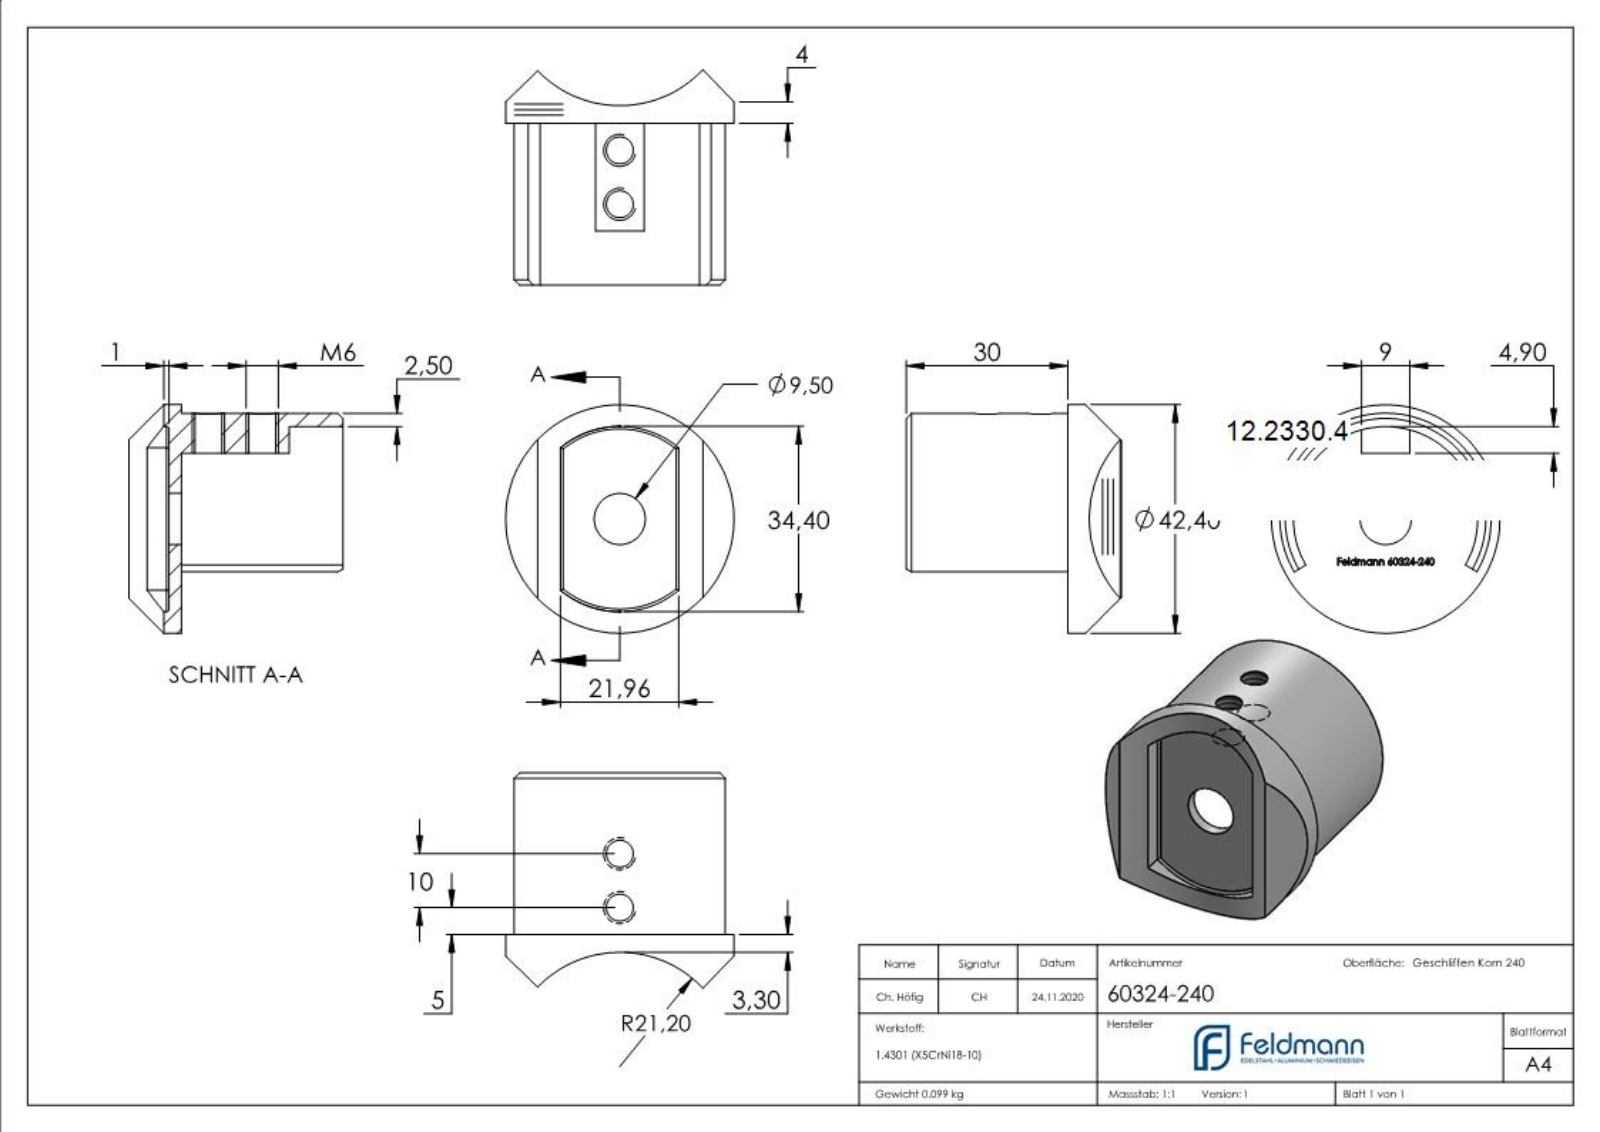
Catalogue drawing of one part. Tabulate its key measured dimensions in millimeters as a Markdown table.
| quantity | value |
| --- | --- |
| part name | 60324-240 |
| STEP written by | SolidWorks 2018 (CONFIG_CONTROL_DESIGN) |
| units | millimeters |
| bodies | 1 solid, 323 faces (173 planar, 19 cylindrical, 131 other) |
| overall size | 42.4 × 42.4 × 39.97 |
| volume | 12 588 mm³ |
| surface area | 9 048 mm² |
| round holes (diameter × count) | 5 × 2, 9.5 × 1 |
| round bosses / shafts (diameter × count) | 42.4 × 1 |
| partial cylindrical surfaces (radius × count) | 0.5 × 2, 17.1 × 1, 17.2 × 1, 19.6 × 1, 21.2 × 1 |
| main face-to-face distances | 2.3, 30, 32.3, 21.96, 9, 10, 20, 22.3, 30.1, 20.1 |
| hole center spacings | 10 |
